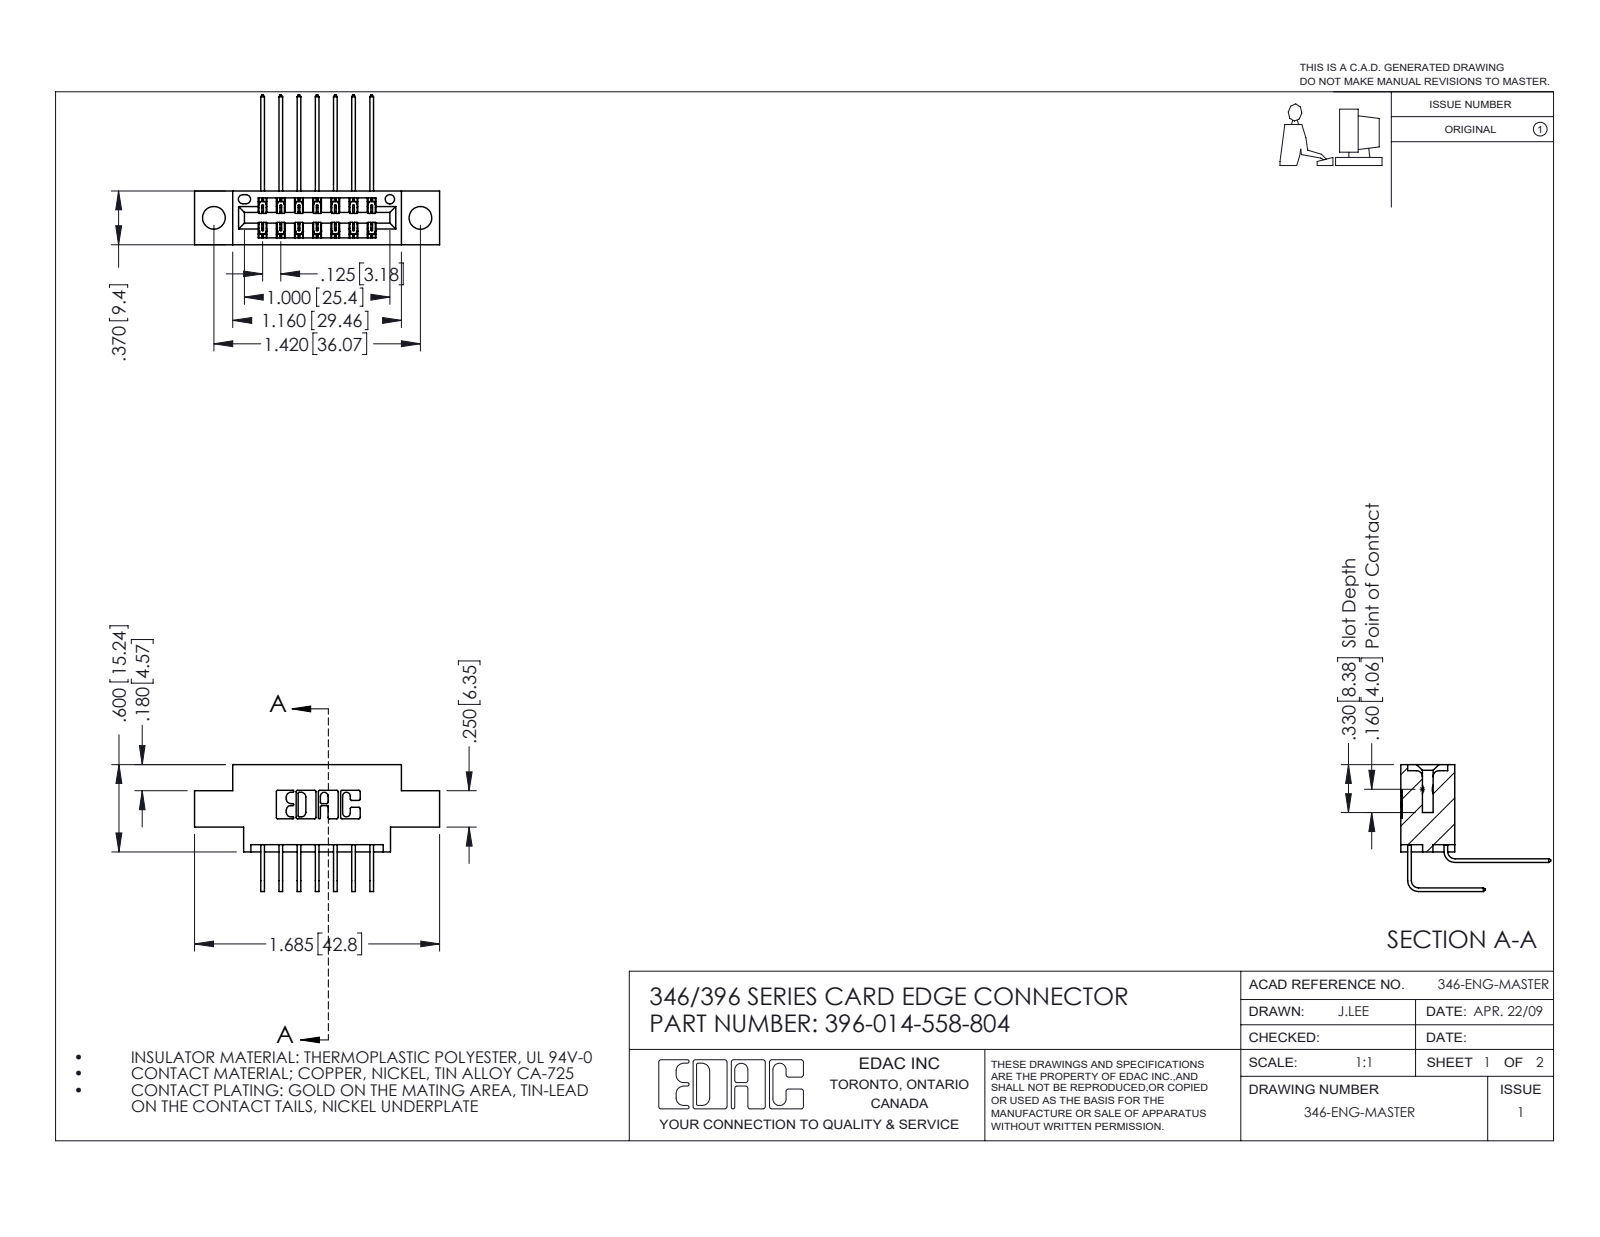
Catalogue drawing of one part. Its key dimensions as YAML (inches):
part_name: "345-292-001_558 Tail - 2; 346 Part_0.170 Offset - 0.156 Dia-TH; 396-014-558-804; 345-292-001_558 559 Tail - 1"
step_written_by: "SolidWorks 2016 (CONFIG_CONTROL_DESIGN)"
units: inches
bodies: {solids: 15, faces: 882, planar: 598, cylindrical: 284, other: 0}
overall_size: [1.685, 1.03, 0.873]
volume: 0.228
surface_area: 7.705
round_holes:
  - {diameter: 0.156, count: 2}
  - {diameter: 0.064, count: 1}
partial_cylinders:
  - {radius: 0.01, count: 22}
  - {radius: 0.006, count: 21}
  - {radius: 0.007, count: 6}
  - {radius: 0.031, count: 6}
  - {radius: 0.026, count: 3}
  - {radius: 0.014, count: 2}
  - {radius: 0.022, count: 2}
  - {radius: 0.024, count: 2}
face_to_face_distances: [0.25, 0.37, 0.048, 0.322, 0.025, 0.072, 0.298, 0.148, 0.222, 0.1]
hole_center_spacings: [0.246, 1.217, 1.42]
